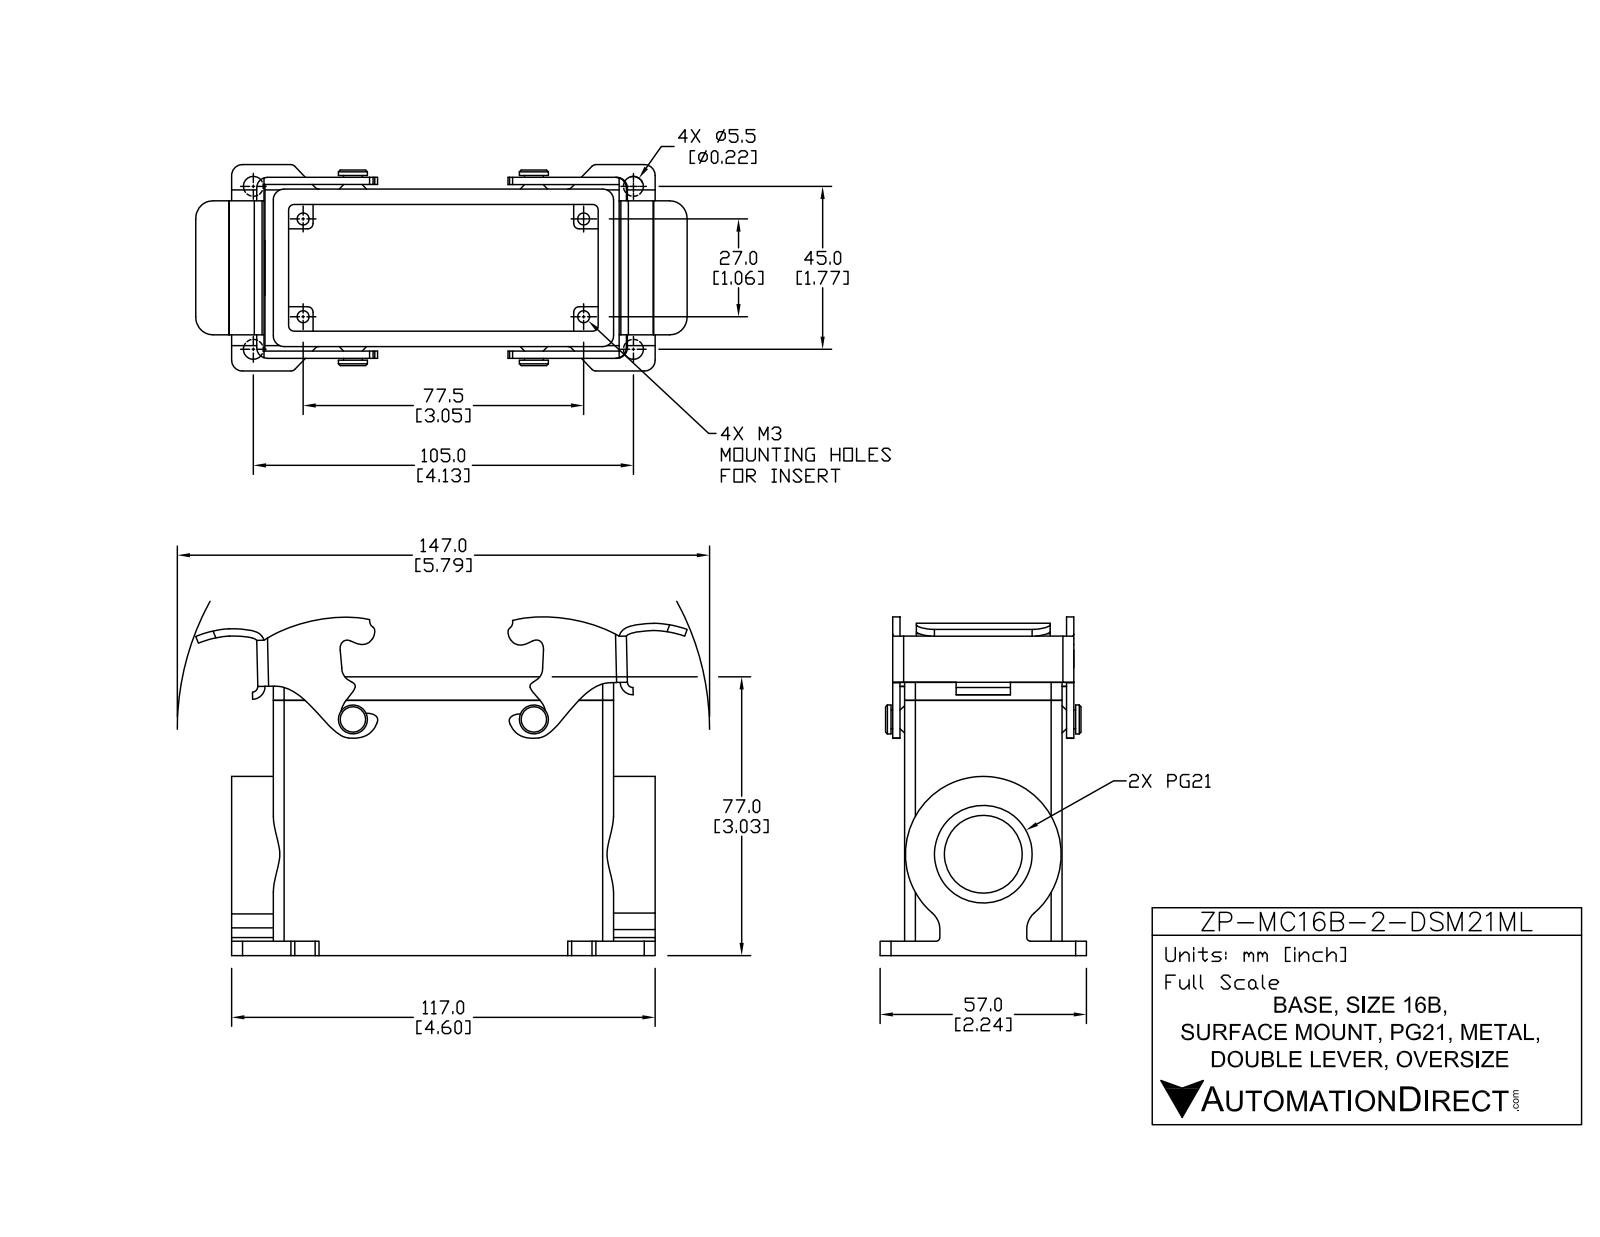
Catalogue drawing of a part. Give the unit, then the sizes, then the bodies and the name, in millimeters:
Units: millimetres
Overall size (bounding box): 145.82 × 89.42 × 57
Round holes (diameter × count): ⌀3.3 ×4, ⌀5.5 ×4, ⌀21.5 ×1, ⌀27 ×1
Round bosses / shafts (diameter × count): ⌀8 ×2, ⌀5.17 ×2
Partial cylindrical surfaces — rounded edges, fillets, slot ends (radius × count): R1 ×18, R1.5 ×16, R0.5 ×10, R3 ×10, R2 ×6, R4 ×6, R5 ×4, R10 ×4
Main face-to-face distances: 4.25, 39.25, 35, 43.5, 2.5, 6.75, 1.5, 1, 11, 89.75
Hole centre spacings: 16.43, 38.54, 91.69, 98.09, 27, 45, 77.5, 82.07
Volume: 132 363 mm³ · Surface area: 67 705 mm²
Bodies: 4 solids, 317 faces (131 planar, 178 cylindrical, 8 other)
Part name (STEP PRODUCT): ZP-MC16B-2-DSM21ML
STEP written by: SolidWorks 2011 (AUTOMOTIVE_DESIGN)
